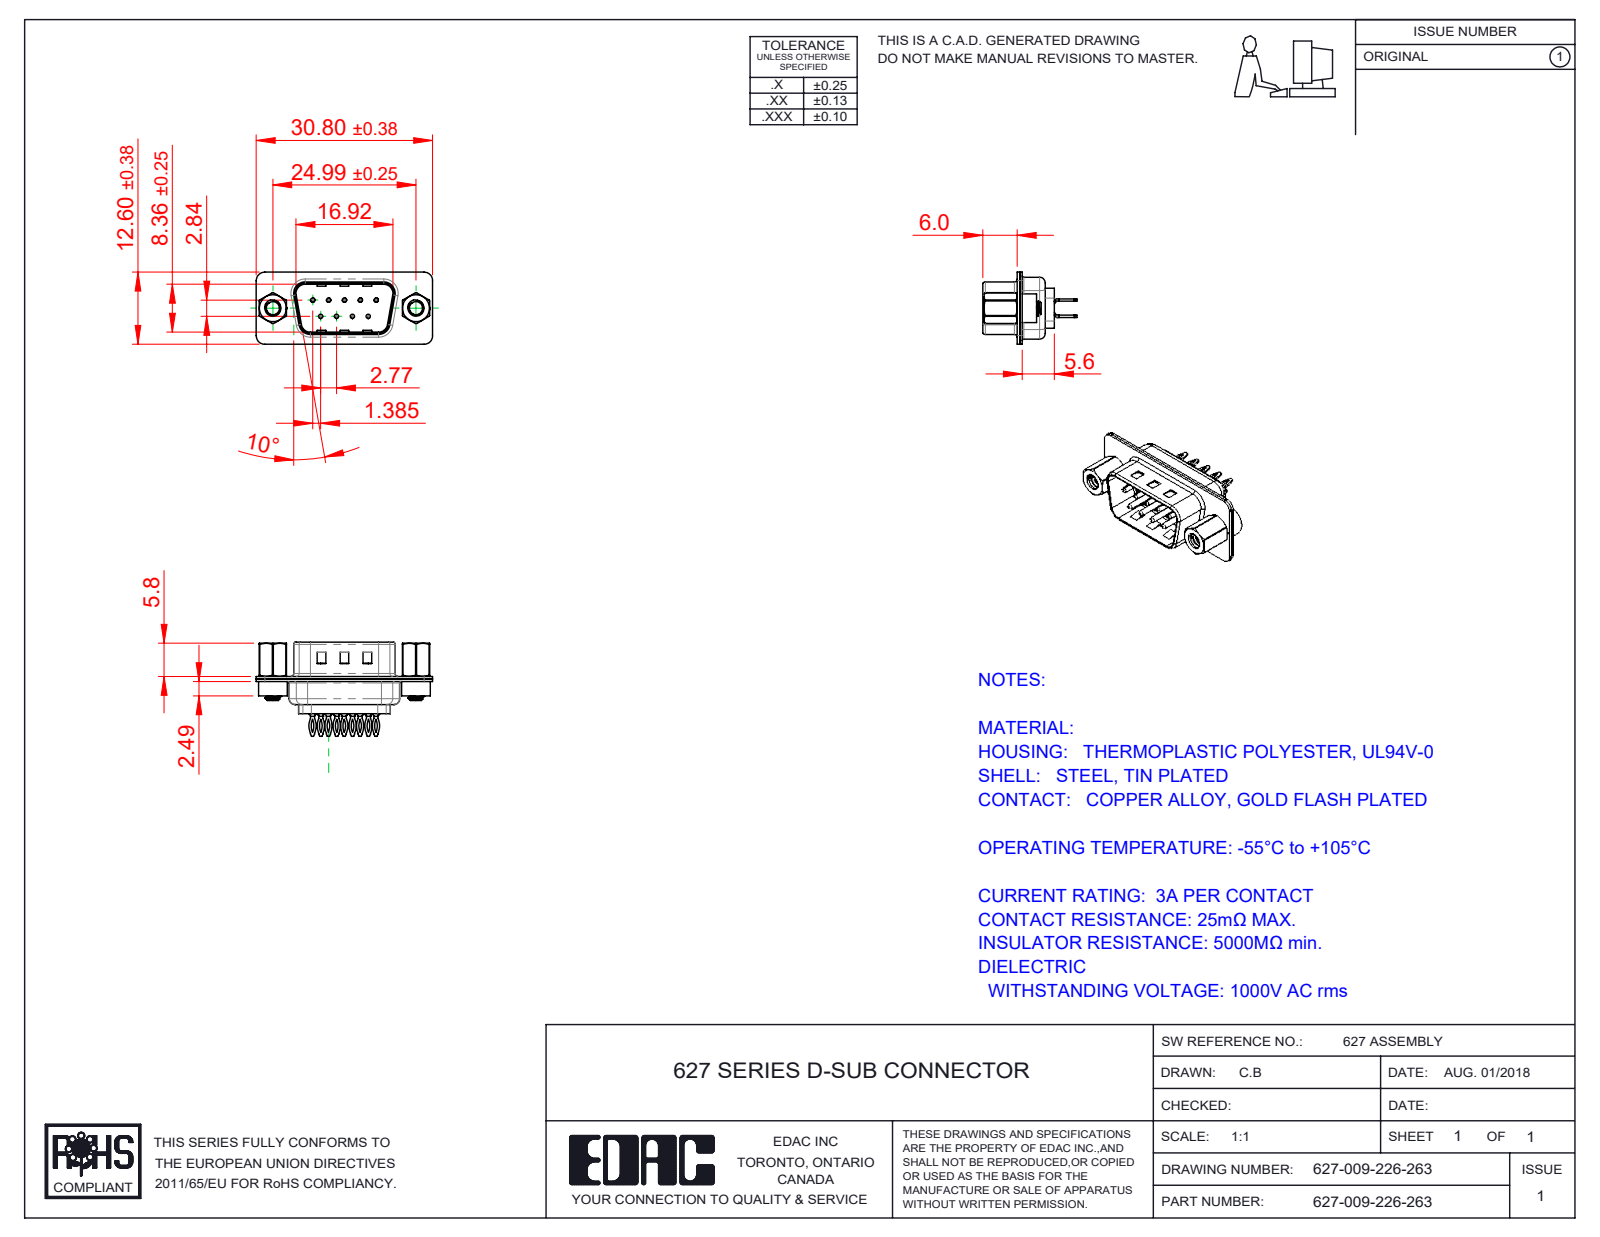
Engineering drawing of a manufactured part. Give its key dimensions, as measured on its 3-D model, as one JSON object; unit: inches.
{"part_name": "627 Housing_09 LP; 627 4-40 Hex Standoff; 627 4-40 Threaded Rivet; 627 Shell Front_09 Contacts (+4 more)", "step_written_by": "SolidWorks 2020 (CONFIG_CONTROL_DESIGN)", "units": "inches", "bodies": {"solids": 16, "faces": 1110, "planar": 309, "cylindrical": 478, "other": 323}, "overall_size": [1.213, 0.648, 0.496], "volume_in3": 0.093, "surface_area_in2": 6.786, "round_holes": [[0.014, 9], [0.043, 9], [0.063, 9], [0.089, 2], [0.09, 2], [0.157, 2], [0.189, 2]], "round_bosses_or_shafts": [[0.079, 9], [0.059, 9], [0.03, 9], [0.197, 2], [0.193, 2], [0.11, 2]], "partial_cylinders_radius": [[0.059, 18], [0.115, 18], [0.131, 18], [0.079, 12], [0.02, 8], [0.063, 8], [0.01, 4], [0.024, 4]], "face_to_face_distances": [0.018, 0.016, 0.035, 0.032, 0.377, 0.055, 0.345, 0.02, 0.059, 0.238], "hole_center_spacings": [0.124, 0.109, 0.218, 0.198, 0.198, 0.327, 0.294, 0.295]}
